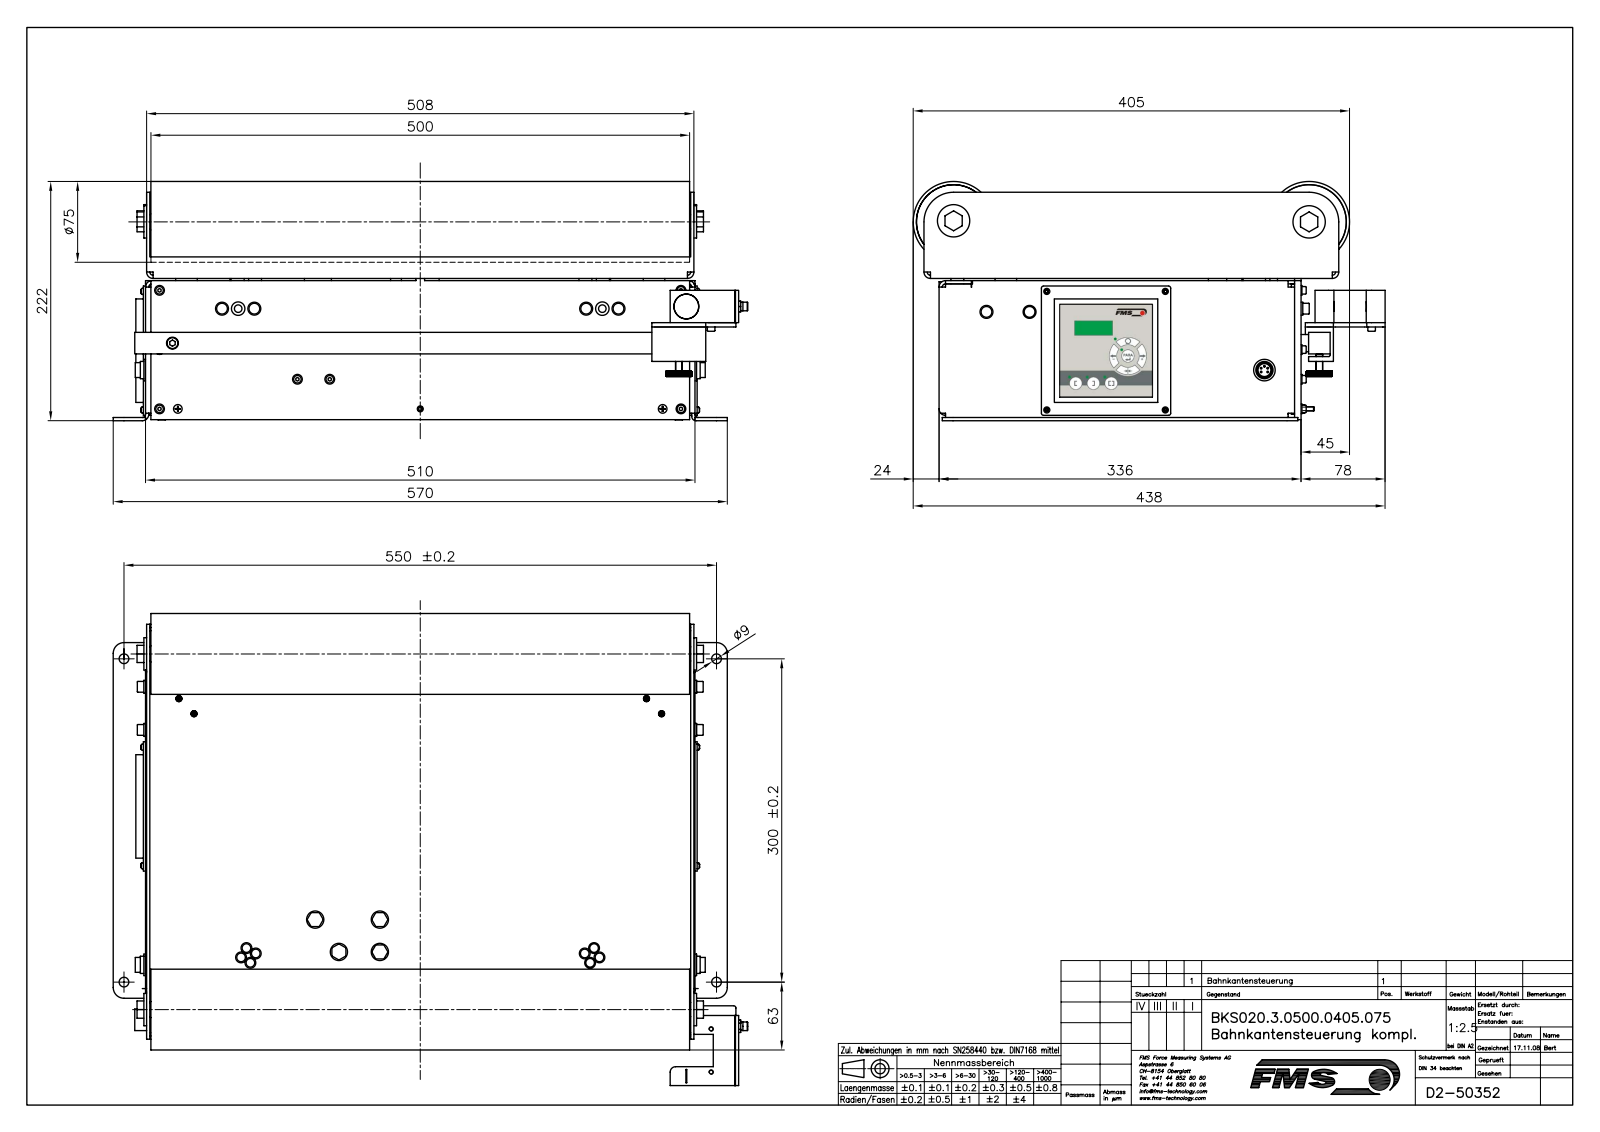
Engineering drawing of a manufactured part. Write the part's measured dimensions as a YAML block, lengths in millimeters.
part_name: "K50352; K49783; K49784; TEIL1 (+8 more)"
step_written_by: "Mechanical Desktop 2007 (CONFIG_CONTROL_DESIGN)"
units: millimeters
bodies: {solids: 170, faces: 6004, planar: 3677, cylindrical: 1851, other: 476}
overall_size: [589.1, 438, 222]
volume: 3962000
surface_area: 2399000
round_holes:
  - {diameter: 3, count: 30}
  - {diameter: 4.3, count: 14}
  - {diameter: 3.42, count: 13}
  - {diameter: 3.2, count: 12}
  - {diameter: 6.4, count: 10}
  - {diameter: 2.2, count: 8}
  - {diameter: 2.6, count: 8}
  - {diameter: 5.3, count: 8}
  - {diameter: 3.5, count: 7}
  - {diameter: 6, count: 6}
  - {diameter: 8.4, count: 6}
  - {diameter: 1, count: 4}
round_bosses_or_shafts:
  - {diameter: 10, count: 20}
  - {diameter: 4, count: 18}
  - {diameter: 8, count: 15}
  - {diameter: 6, count: 13}
  - {diameter: 12, count: 10}
  - {diameter: 7, count: 10}
  - {diameter: 9, count: 8}
  - {diameter: 5, count: 8}
partial_cylinders:
  - {radius: 0.32, count: 48}
  - {radius: 1, count: 29}
  - {radius: 0.25, count: 24}
  - {radius: 0.56, count: 24}
  - {radius: 2, count: 24}
  - {radius: 0.2, count: 20}
  - {radius: 0.25, count: 19}
  - {radius: 3, count: 14}
face_to_face_distances: [3, 1, 127, 130, 128, 131, 2, 5, 4, 506]
hole_center_spacings: [97.87, 10, 83.5, 97.44, 324.04, 110, 314.04, 15]
